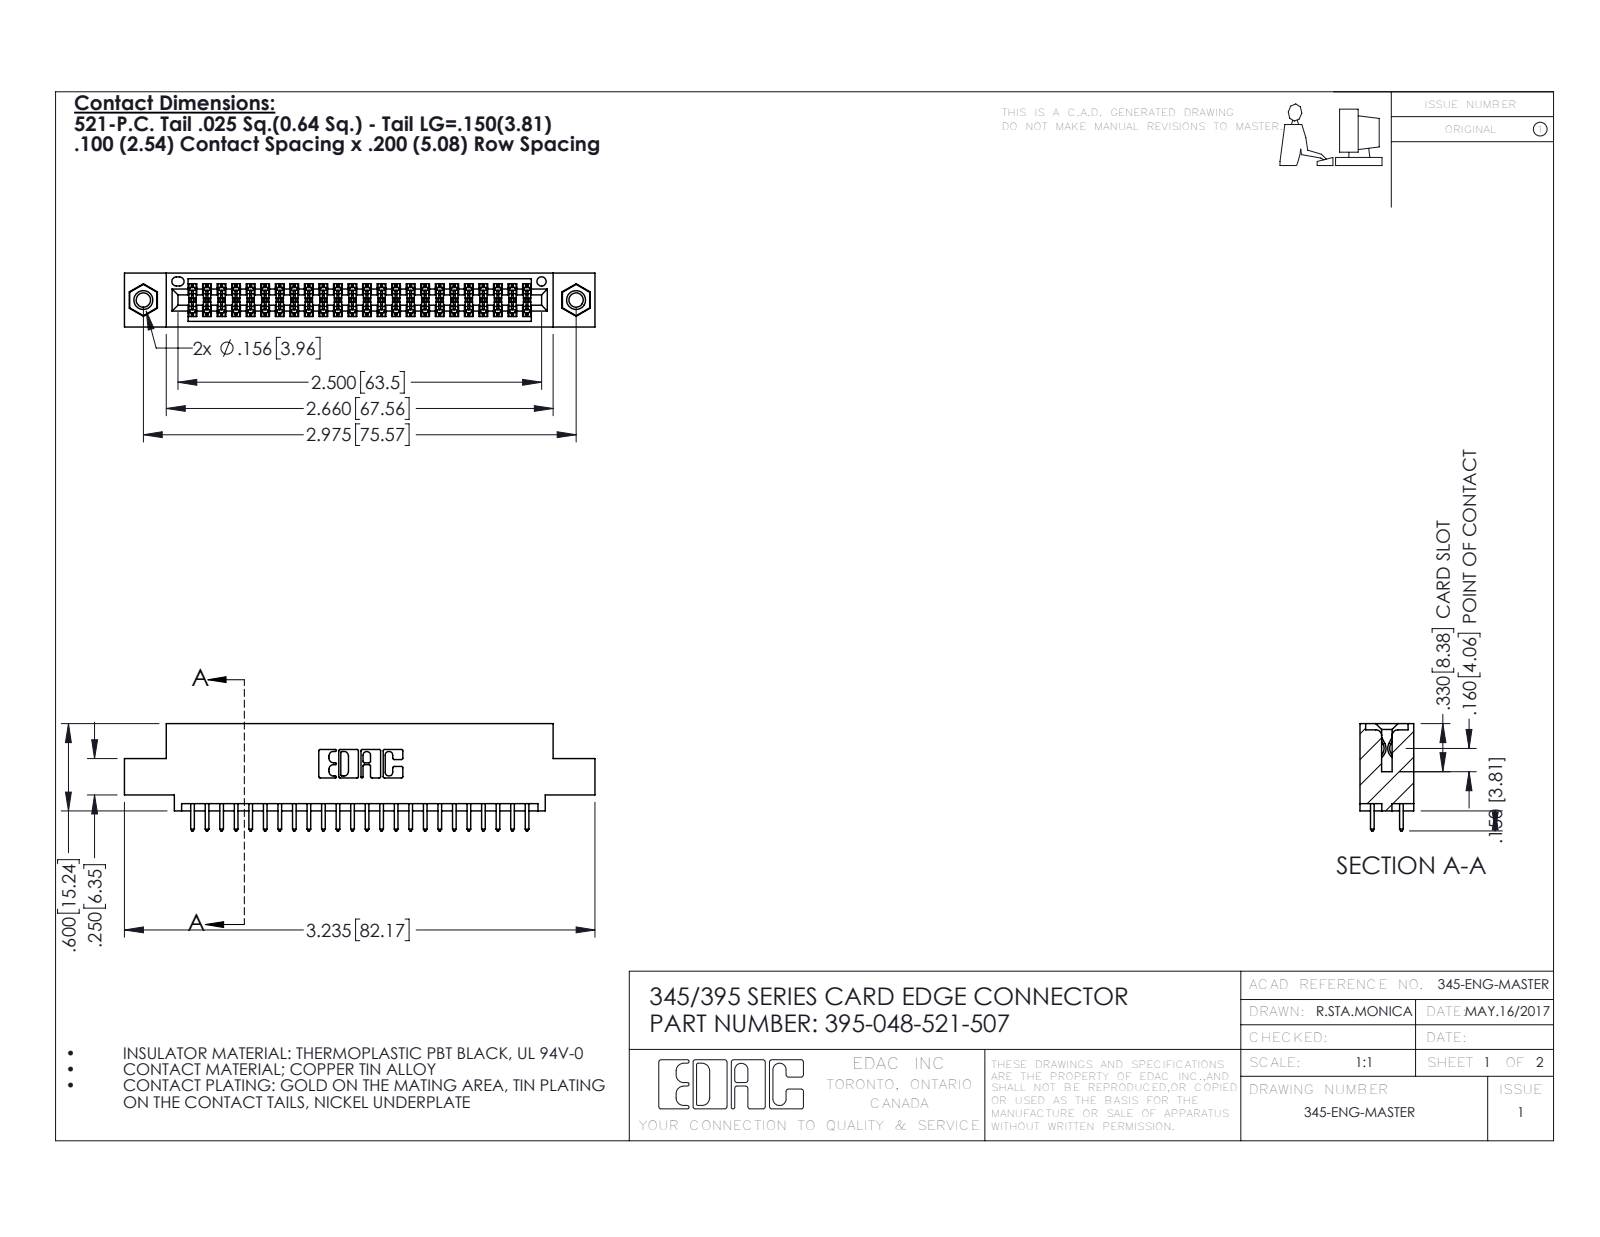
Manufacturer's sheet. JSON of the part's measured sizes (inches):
{"part_name": "345 Part_0.110 Offset - 0.156 Dia-TI; 345-250-001_345-250-005-103; 345-292-001_345-293-121; 395-048-521-507", "step_written_by": "SolidWorks 2016 (CONFIG_CONTROL_DESIGN)", "units": "inches", "bodies": {"solids": 51, "faces": 2590, "planar": 1700, "cylindrical": 874, "other": 16}, "overall_size": [3.235, 0.737, 0.37], "volume_in3": 0.47, "surface_area_in2": 17.11, "round_holes": [[0.098, 2], [0.125, 2], [0.156, 2], [0.064, 1]], "round_bosses_or_shafts": [[0.155, 2]], "partial_cylinders_radius": [[0.006, 72], [0.01, 48], [0.01, 22], [0.007, 6], [0.031, 6], [0.026, 3], [0.014, 2], [0.019, 2]], "face_to_face_distances": [0.072, 0.298, 0.2, 0.37, 0.098, 0.272, 0.025, 0.225, 0.175, 0.149], "hole_center_spacings": [0.27, 2.741, 2.975]}
